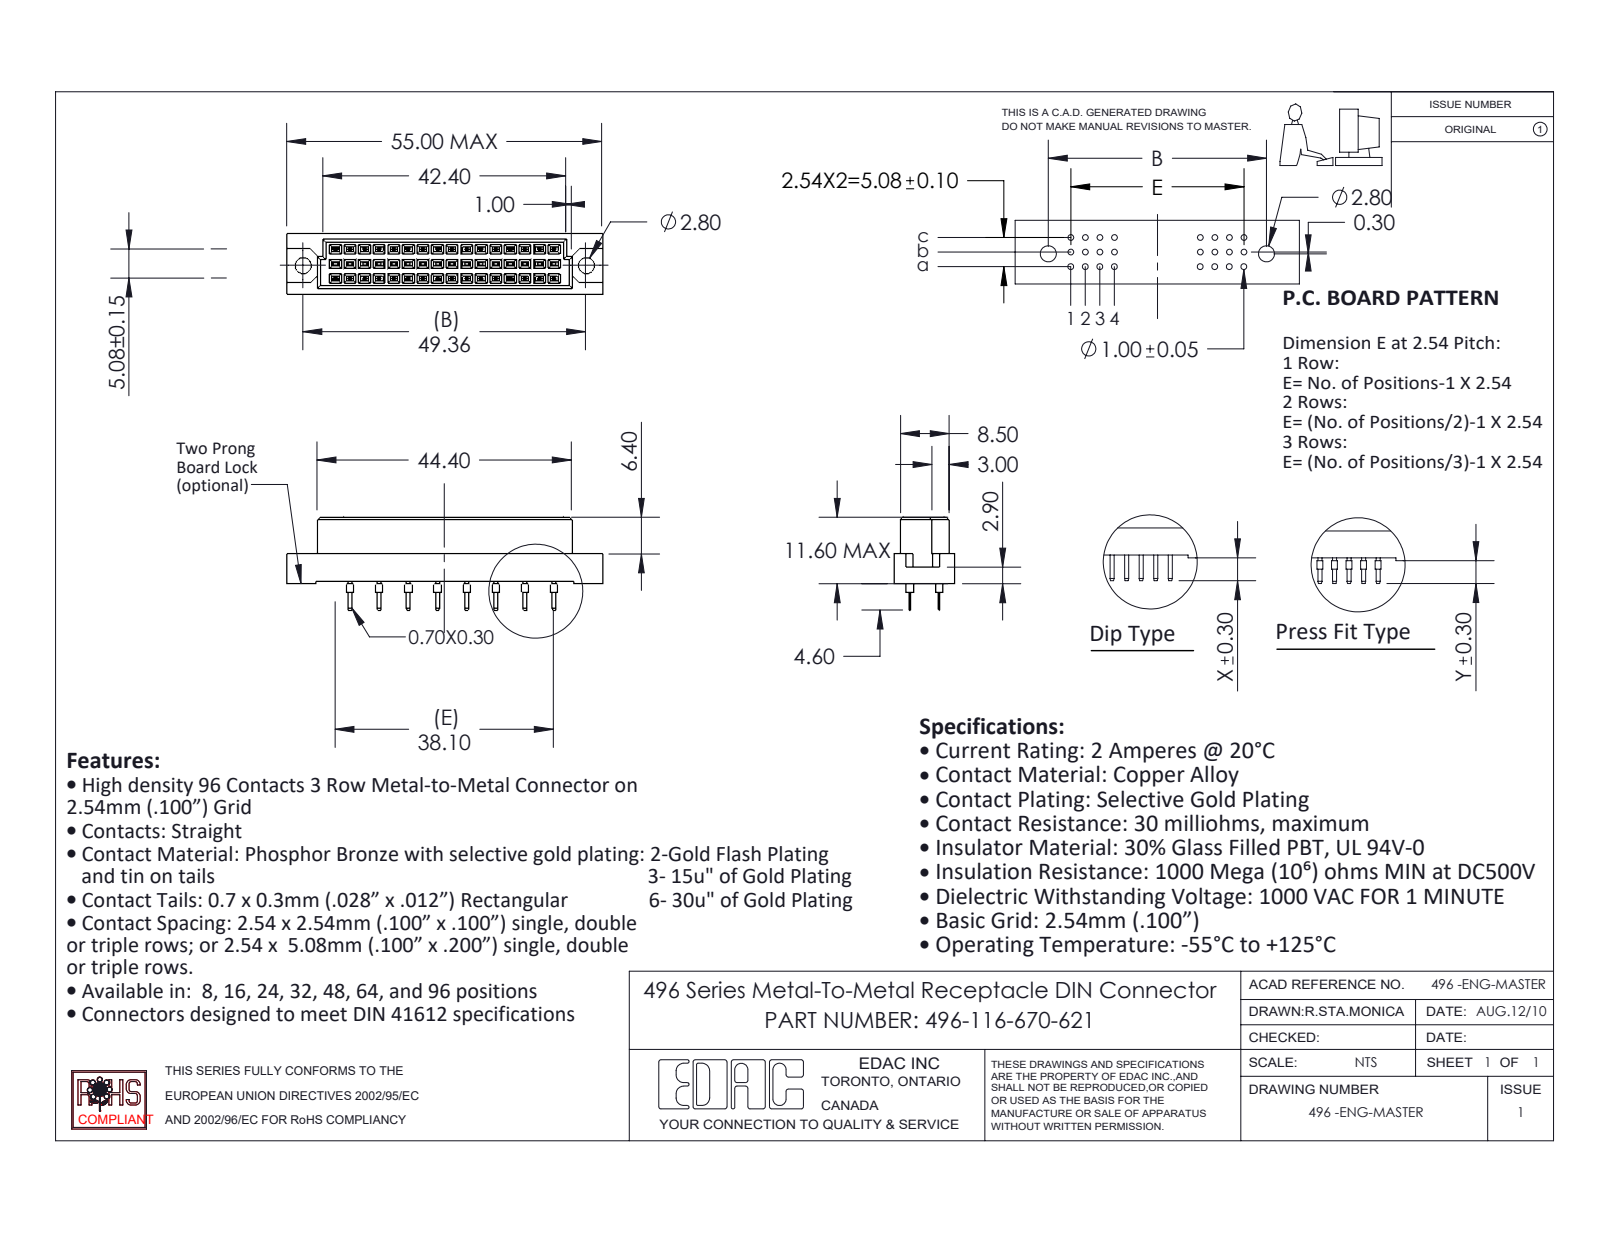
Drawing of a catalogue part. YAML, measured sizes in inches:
part_name: "496-116-670-621; 496 Part_48; 496-290_70"
step_written_by: "SolidWorks 2020 (CONFIG_CONTROL_DESIGN)"
units: inches
bodies: {solids: 17, faces: 954, planar: 918, cylindrical: 36, other: 0}
overall_size: [2.165, 0.638, 0.417]
volume: 0.283
surface_area: 7.056
round_holes:
  - {diameter: 0.11, count: 2}
round_bosses_or_shafts:
  - {diameter: 0.039, count: 16}
face_to_face_distances: [0.1, 0.2, 0.041, 0.376, 0.032, 0.417, 0.022, 0.132, 0.068, 0.335]
hole_center_spacings: [1.943]
